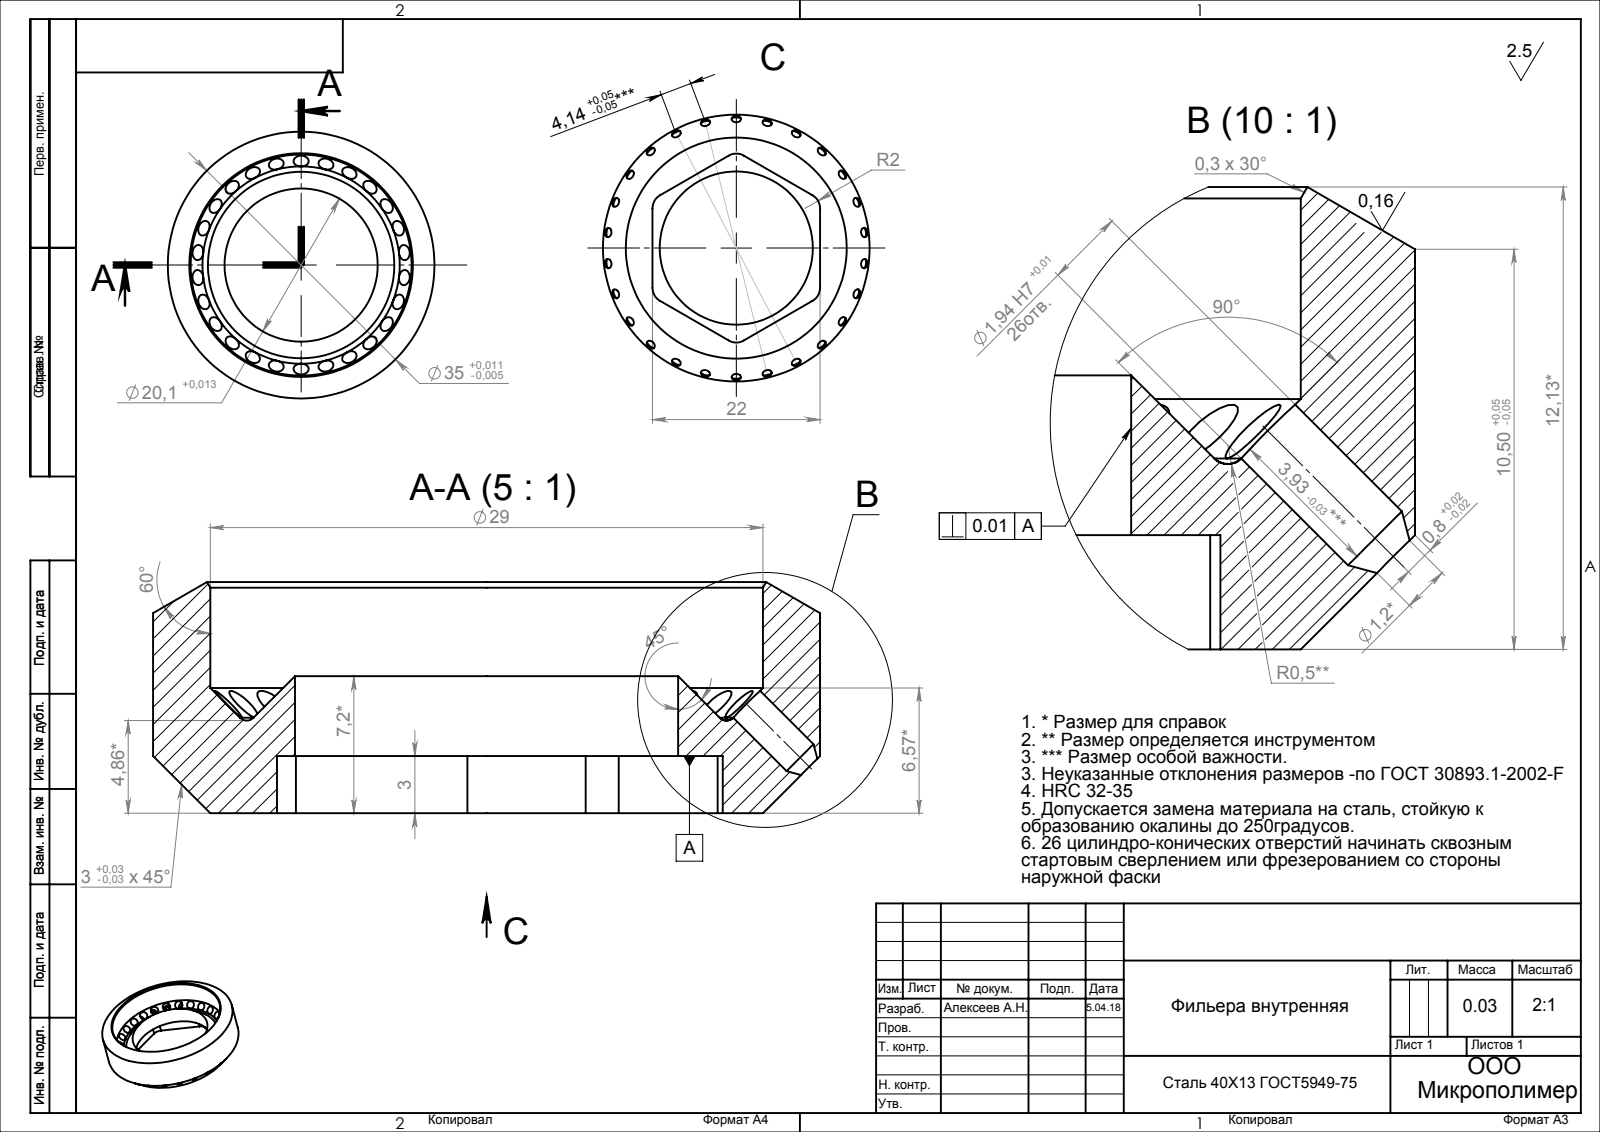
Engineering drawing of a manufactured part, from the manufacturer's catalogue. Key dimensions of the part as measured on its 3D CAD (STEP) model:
Part name (STEP PRODUCT): Vnutr2-2
STEP written by: SolidWorks 2016 (CONFIG_CONTROL_DESIGN)
Units: millimetres
Bodies: 1 solid, 137 faces (8 planar, 65 cylindrical, 64 other)
Overall size (bounding box): 35 × 35 × 12.13
Volume: 4 270 mm³ · Surface area: 4 034 mm²
Round holes (diameter × count): ⌀2 ×26, ⌀20.1 ×1, ⌀29 ×1
Round bosses / shafts (diameter × count): ⌀35 ×1
Partial cylindrical surfaces — rounded edges, fillets, slot ends (radius × count): R2 ×6
Main face-to-face distances: 3, 22
